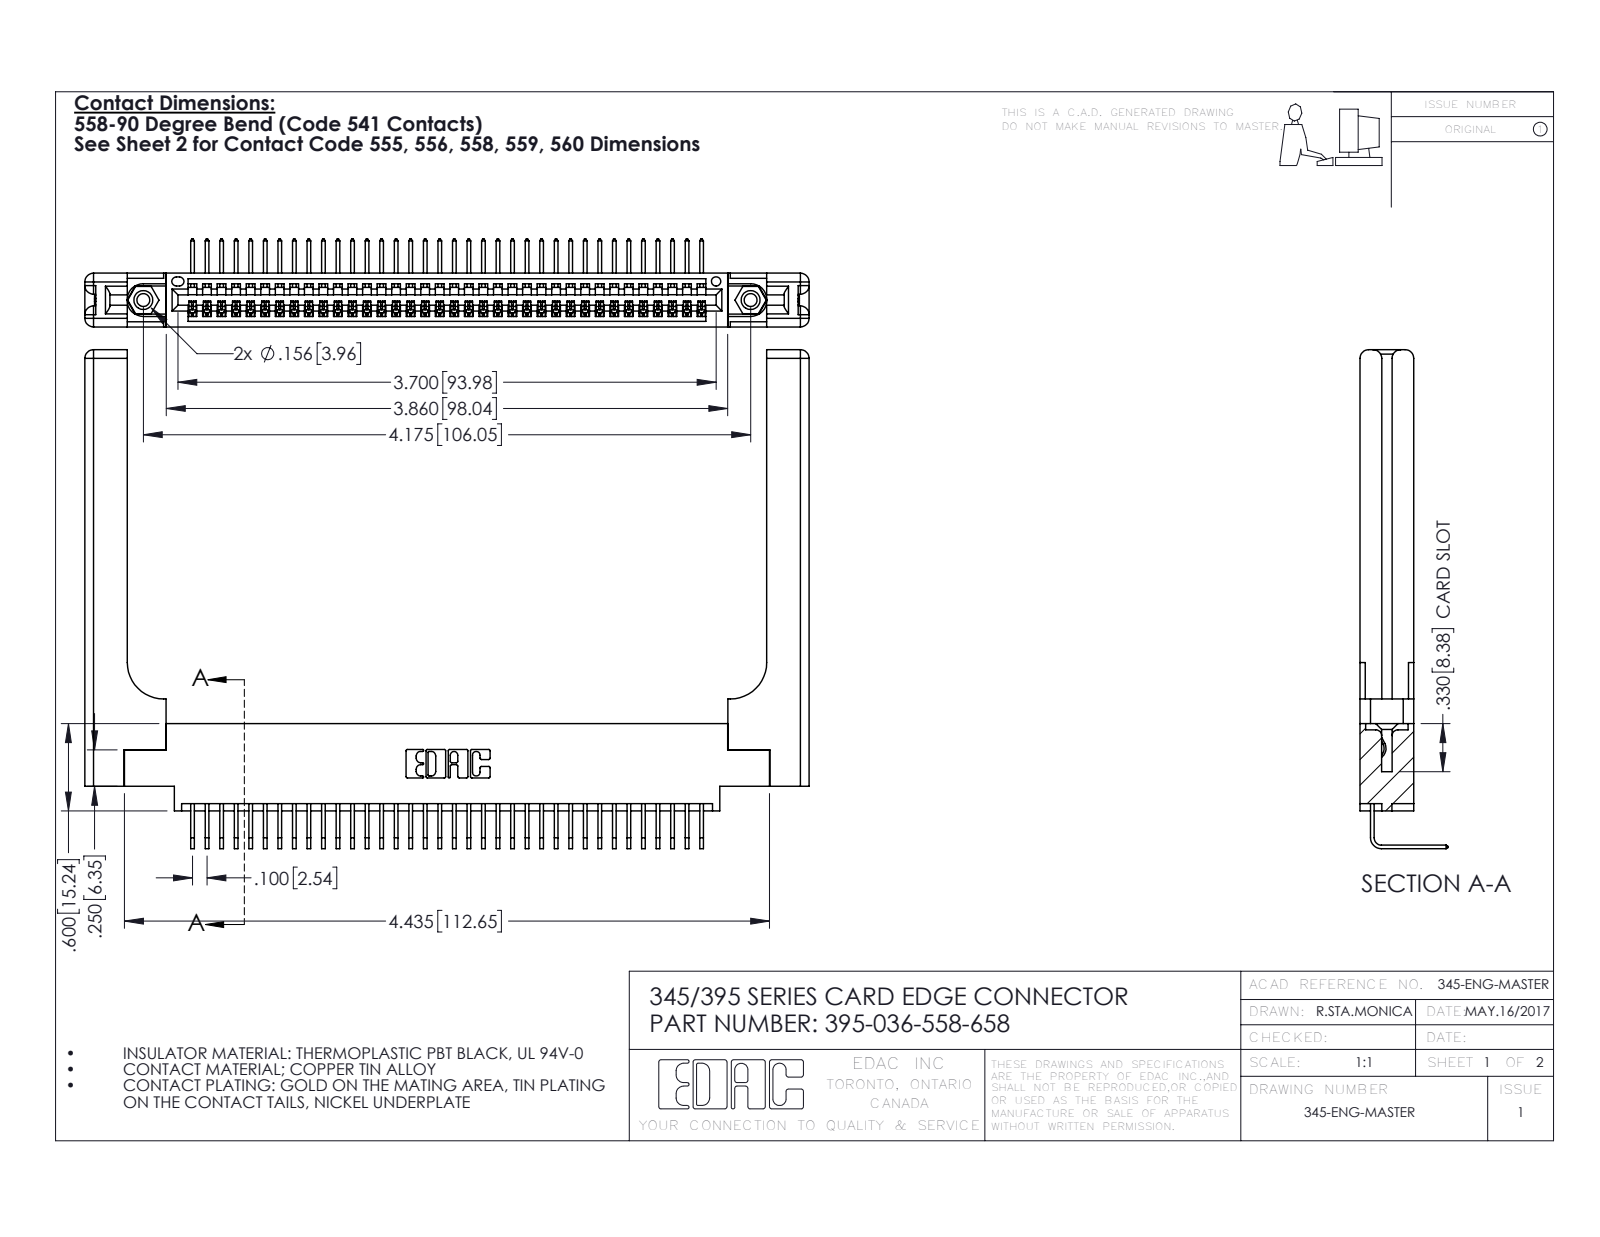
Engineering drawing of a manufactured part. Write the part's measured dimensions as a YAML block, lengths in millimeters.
part_name: "345-250-001_345-250-001-102; 345 Part_0.170 Offset - 0.156 Dia-TH; 345-220-058_345-220-058; 345-292-001_558 Tail - 2 (+1 more)"
step_written_by: "SolidWorks 2016 (CONFIG_CONTROL_DESIGN)"
units: millimeters
bodies: {solids: 41, faces: 2546, planar: 1744, cylindrical: 742, other: 60}
overall_size: [126.5, 87.1, 15.4]
volume: 20470
surface_area: 21960
round_holes:
  - {diameter: 2.3, count: 2}
  - {diameter: 3.2, count: 2}
  - {diameter: 4, count: 2}
  - {diameter: 1.6, count: 1}
round_bosses_or_shafts:
  - {diameter: 3.9, count: 2}
partial_cylinders:
  - {radius: 0.2, count: 72}
  - {radius: 0.3, count: 22}
  - {radius: 1.5, count: 16}
  - {radius: 0.2, count: 6}
  - {radius: 0.8, count: 6}
  - {radius: 0.7, count: 3}
  - {radius: 0.8, count: 2}
  - {radius: 0.8, count: 2}
face_to_face_distances: [9.4, 1.8, 7.6, 2.5, 6.9, 0.6, 5.1, 3.8, 3.8, 5.7]
hole_center_spacings: [6.9, 100.1, 106]
